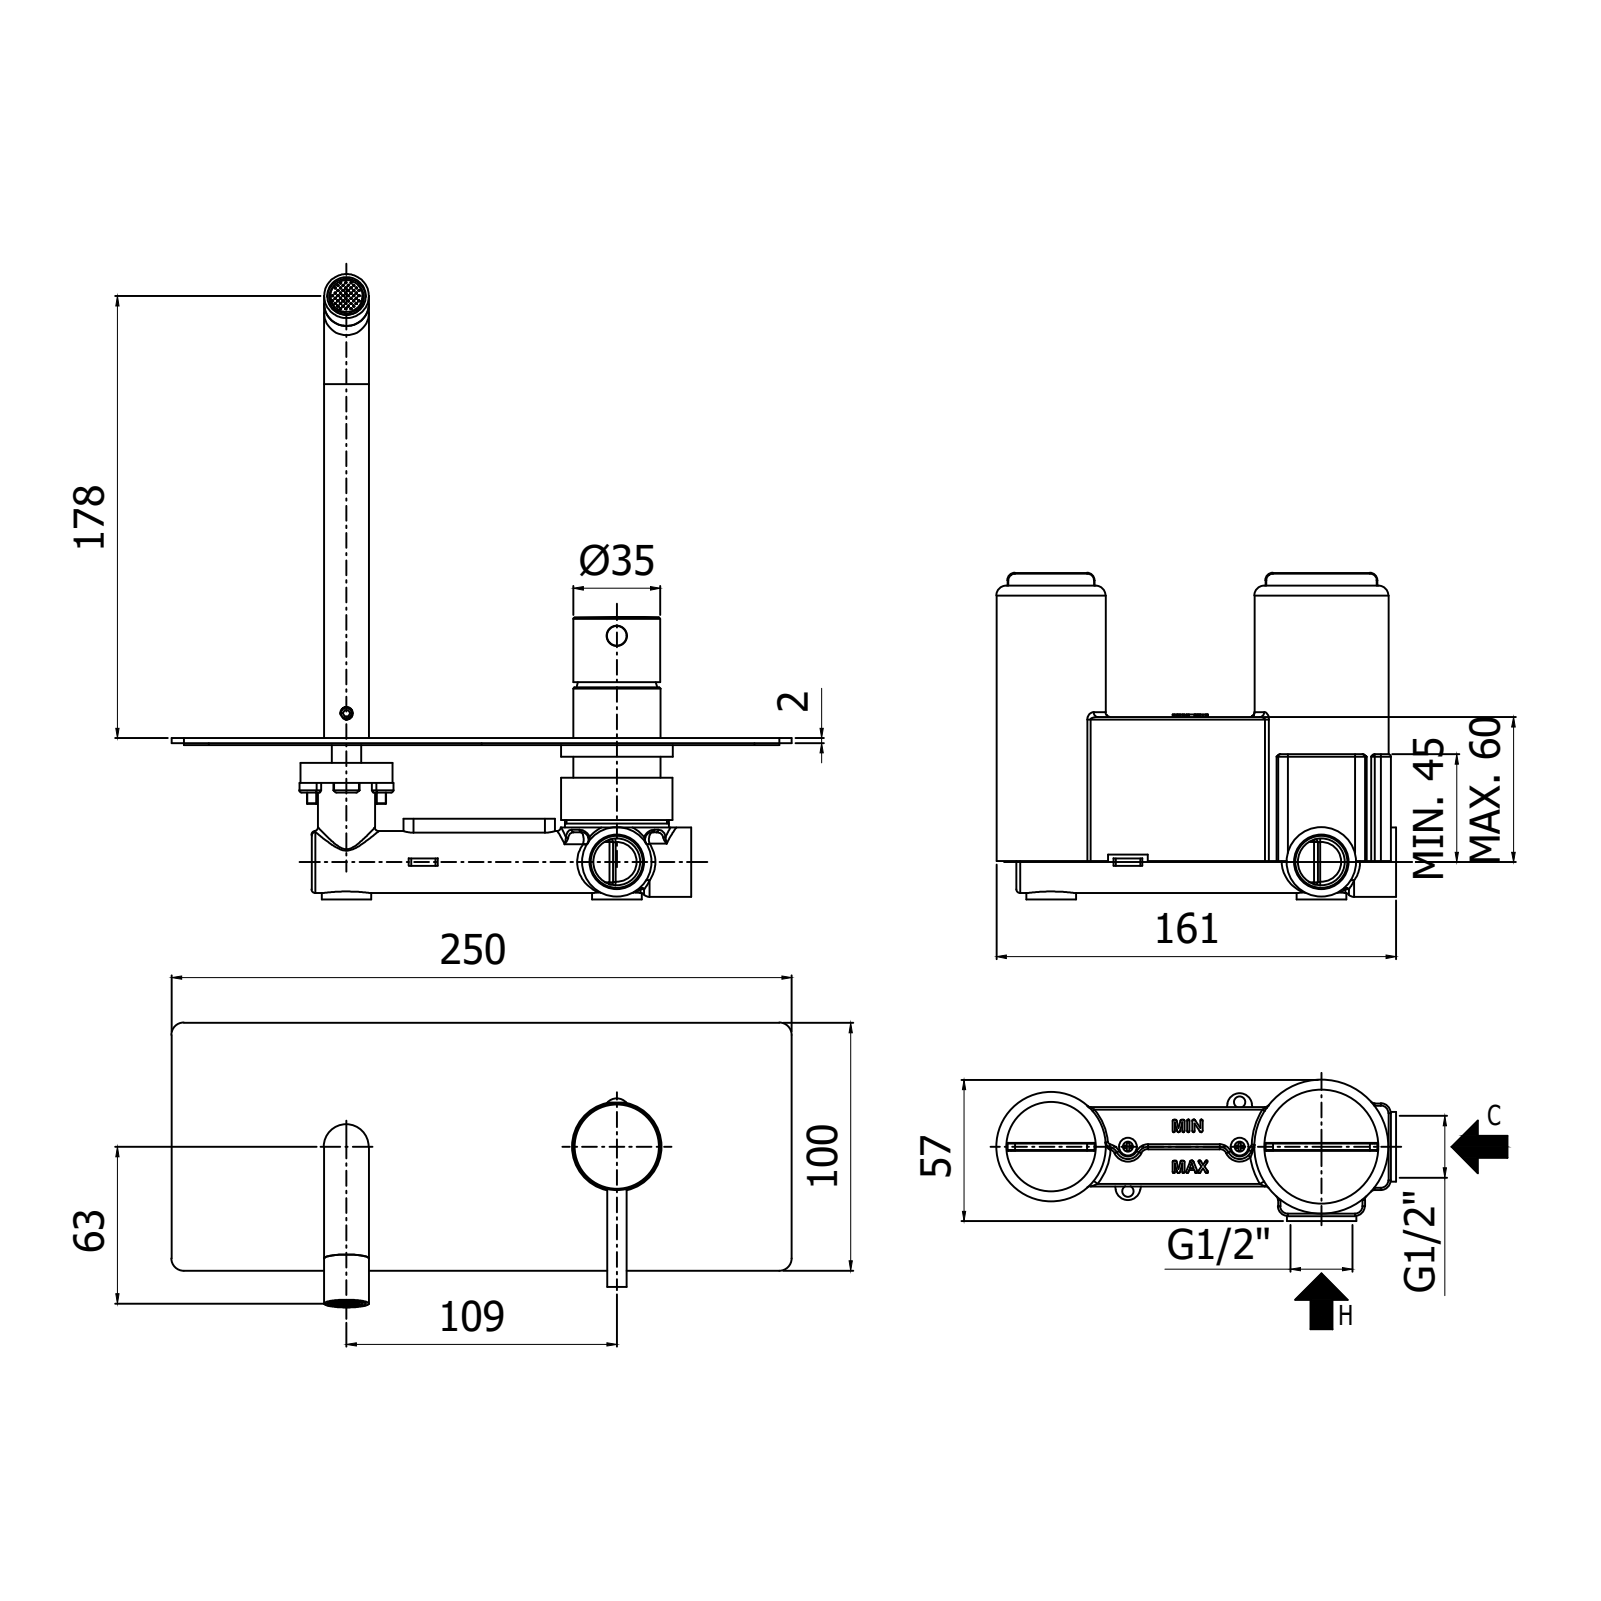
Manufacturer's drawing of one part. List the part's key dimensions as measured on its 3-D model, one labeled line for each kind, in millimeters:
Part name (STEP PRODUCT): SK105CR
STEP written by: CREO PARAMETRIC BY PTC INC, 2020044 (CONFIG_CONTROL_DESIGN)
Units: millimetres
Bodies: 2 solids, 953 faces (238 planar, 485 cylindrical, 230 other)
Overall size (bounding box): 250 × 189.08 × 114.78
Volume: 115 450 mm³ · Surface area: 97 285 mm²
Round holes (diameter × count): ⌀0.5 ×51, ⌀4.2 ×2, ⌀10 ×2, ⌀11 ×2, ⌀12 ×2, ⌀3 ×1, ⌀6 ×1, ⌀8.1 ×1, ⌀13 ×1, ⌀14 ×1, ⌀15 ×1, ⌀15.5 ×1
Round bosses / shafts (diameter × count): ⌀18 ×2, ⌀5 ×2, ⌀35.2 ×1, ⌀35 ×1, ⌀30 ×1, ⌀27.7 ×1, ⌀25 ×1, ⌀23.8 ×1
Partial cylindrical surfaces — rounded edges, fillets, slot ends (radius × count): R0.5 ×58, R1 ×21, R5 ×5, R2 ×4, R3 ×4, R3.5 ×3, R1.5 ×2, R5.9 ×2
Main face-to-face distances: 2, 6.5, 5.8, 16, 14, 100, 48.6, 46.6, 32.6, 0.7
Hole centre spacings: 1.5, 3.35, 2.12, 4.74, 3, 4.24, 4.5, 6.71
